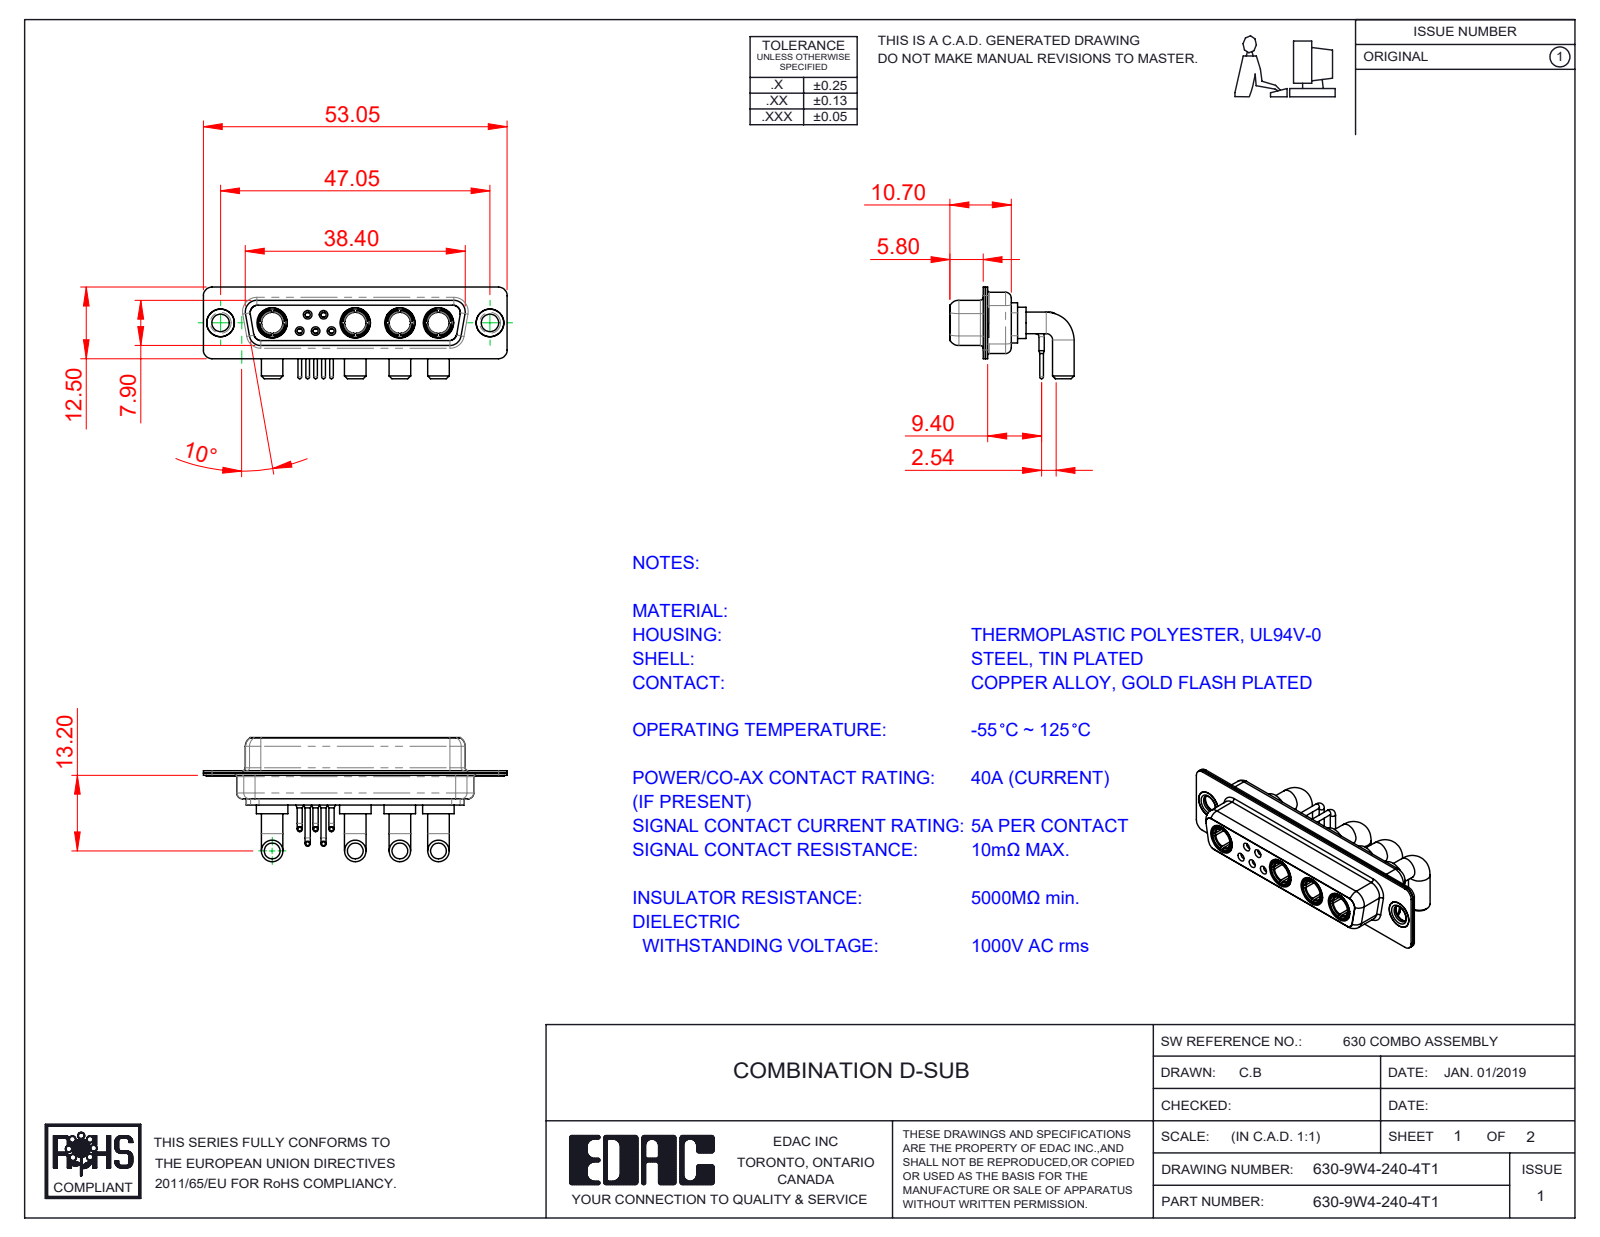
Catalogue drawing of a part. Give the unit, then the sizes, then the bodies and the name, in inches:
Units: inches
Overall size (bounding box): 2.089 × 0.854 × 0.63
Round holes (diameter × count): ⌀0.191 ×6, ⌀0.035 ×5, ⌀0.043 ×5, ⌀0.059 ×5, ⌀0.079 ×5, ⌀0.146 ×4, ⌀0.209 ×4, ⌀0.063 ×3, ⌀0.067 ×2, ⌀0.12 ×2, ⌀0.157 ×2, ⌀0.159 ×2
Round bosses / shafts (diameter × count): ⌀0.148 ×8, ⌀0.035 ×5, ⌀0.026 ×5, ⌀0.217 ×4, ⌀0.205 ×4, ⌀0.195 ×4, ⌀0.187 ×4, ⌀0.197 ×2
Partial cylindrical surfaces — rounded edges, fillets, slot ends (radius × count): R0.059 ×16, R0.079 ×12, R0.053 ×8, R0.063 ×8, R0.01 ×4, R0.02 ×4, R0.024 ×4, R0.026 ×4
Main face-to-face distances: 0.016, 0.018, 0.055, 0.333, 0.35, 0.071, 0.244, 0.278, 0.073, 0.295
Hole centre spacings: 0.124, 0.109, 0.173, 0.198, 0.198, 0.198, 0.218, 0.226
Volume: 0.259 in³ · Surface area: 13.76 in²
Bodies: 18 solids, 830 faces (258 planar, 336 cylindrical, 236 other)
Part name (STEP PRODUCT): 630Combo Shell Rear_25 Contacts; 630Combo Housing_9W4; 630-9W4-240-4T1; 630Combo Contact Row 2 (+4 more)
STEP written by: SolidWorks 2020 (CONFIG_CONTROL_DESIGN)
